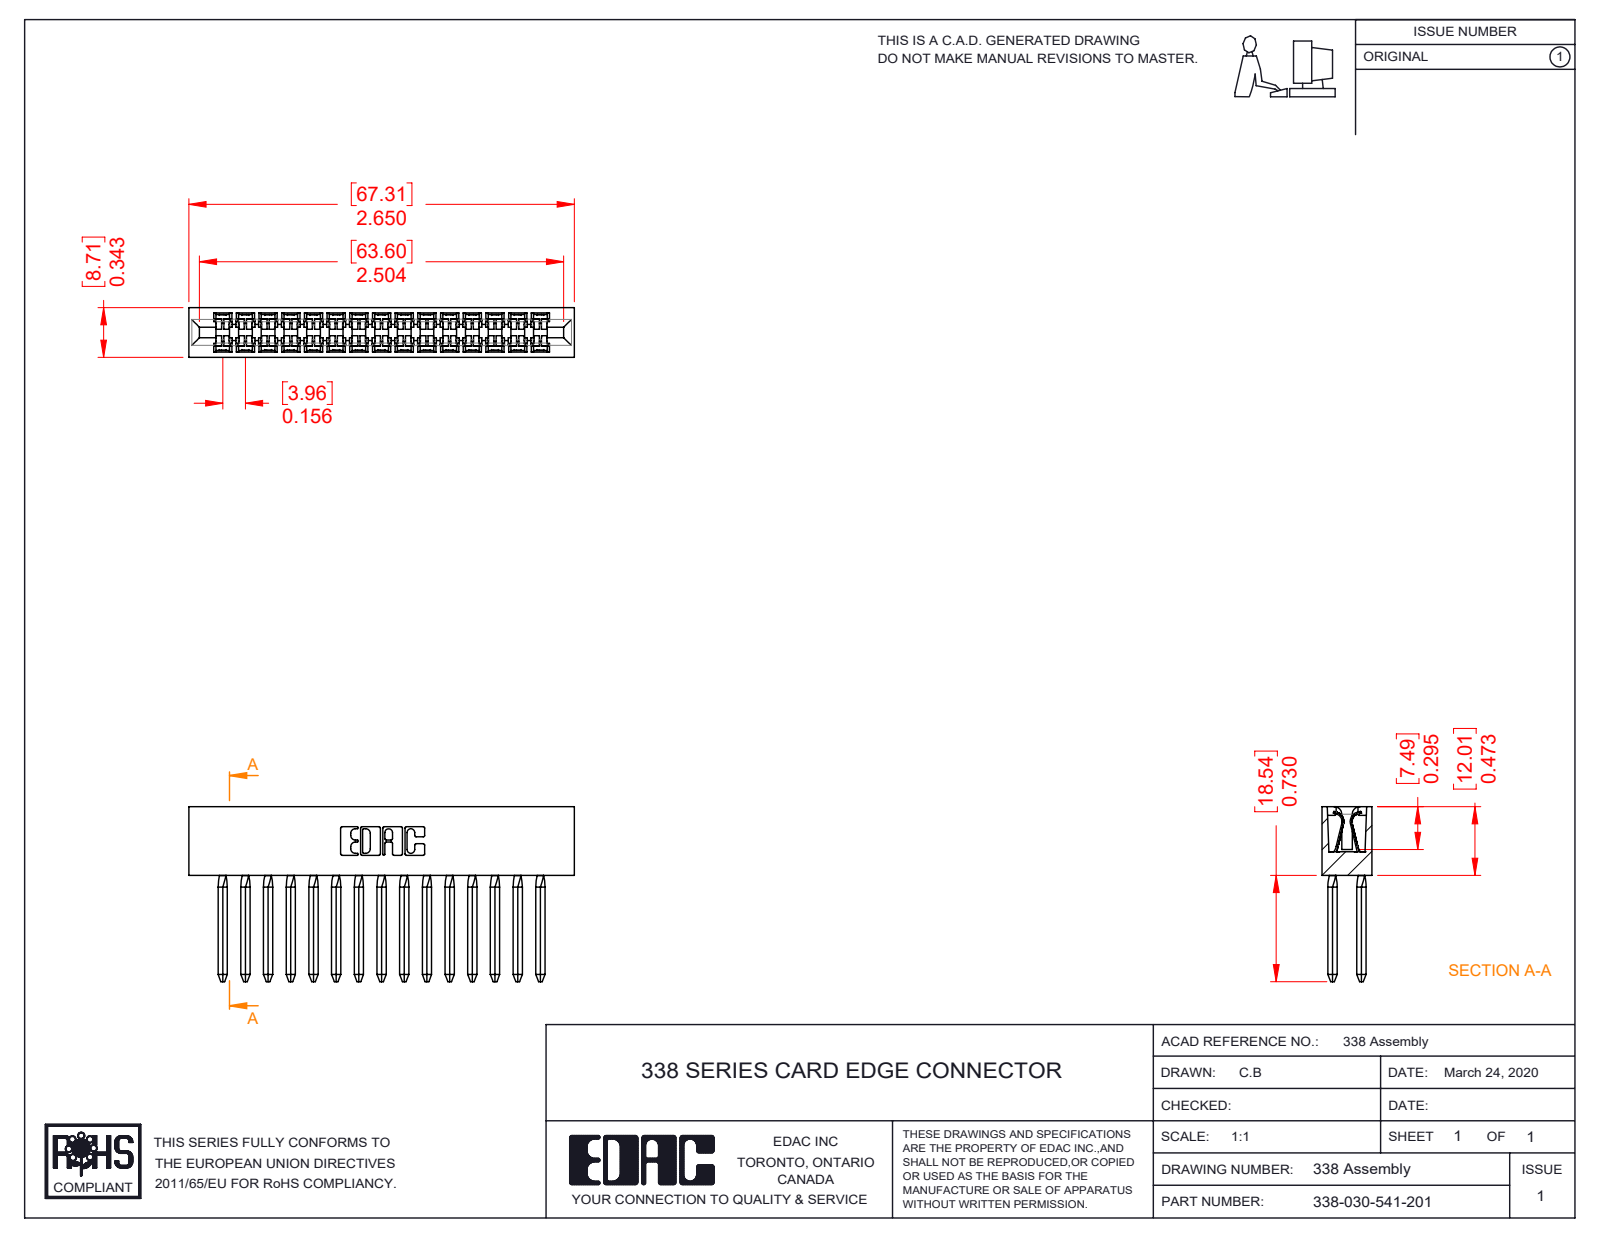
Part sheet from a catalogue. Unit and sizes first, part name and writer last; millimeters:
Units: millimetres
Overall size (bounding box): 67.3 × 30.6 × 8.7
Partial cylindrical surfaces — rounded edges, fillets, slot ends (radius × count): R0.6 ×92, R0.2 ×30, R1.4 ×24, R1.7 ×24, R2.5 ×24, R0.3 ×22, R0.2 ×6, R0.8 ×6
Main face-to-face distances: 8.7, 4, 2.8, 15.8, 11.9, 7.9, 5.6, 19.8, 3.4, 5.3
Volume: 5 490 mm³ · Surface area: 10 280 mm²
Bodies: 31 solids, 2096 faces (1456 planar, 520 cylindrical, 120 other)
Part name (STEP PRODUCT): 338-210-001_338-210-015-001; 338-030-541-201; 338-290-001_541
STEP written by: SolidWorks 2016 (CONFIG_CONTROL_DESIGN)
